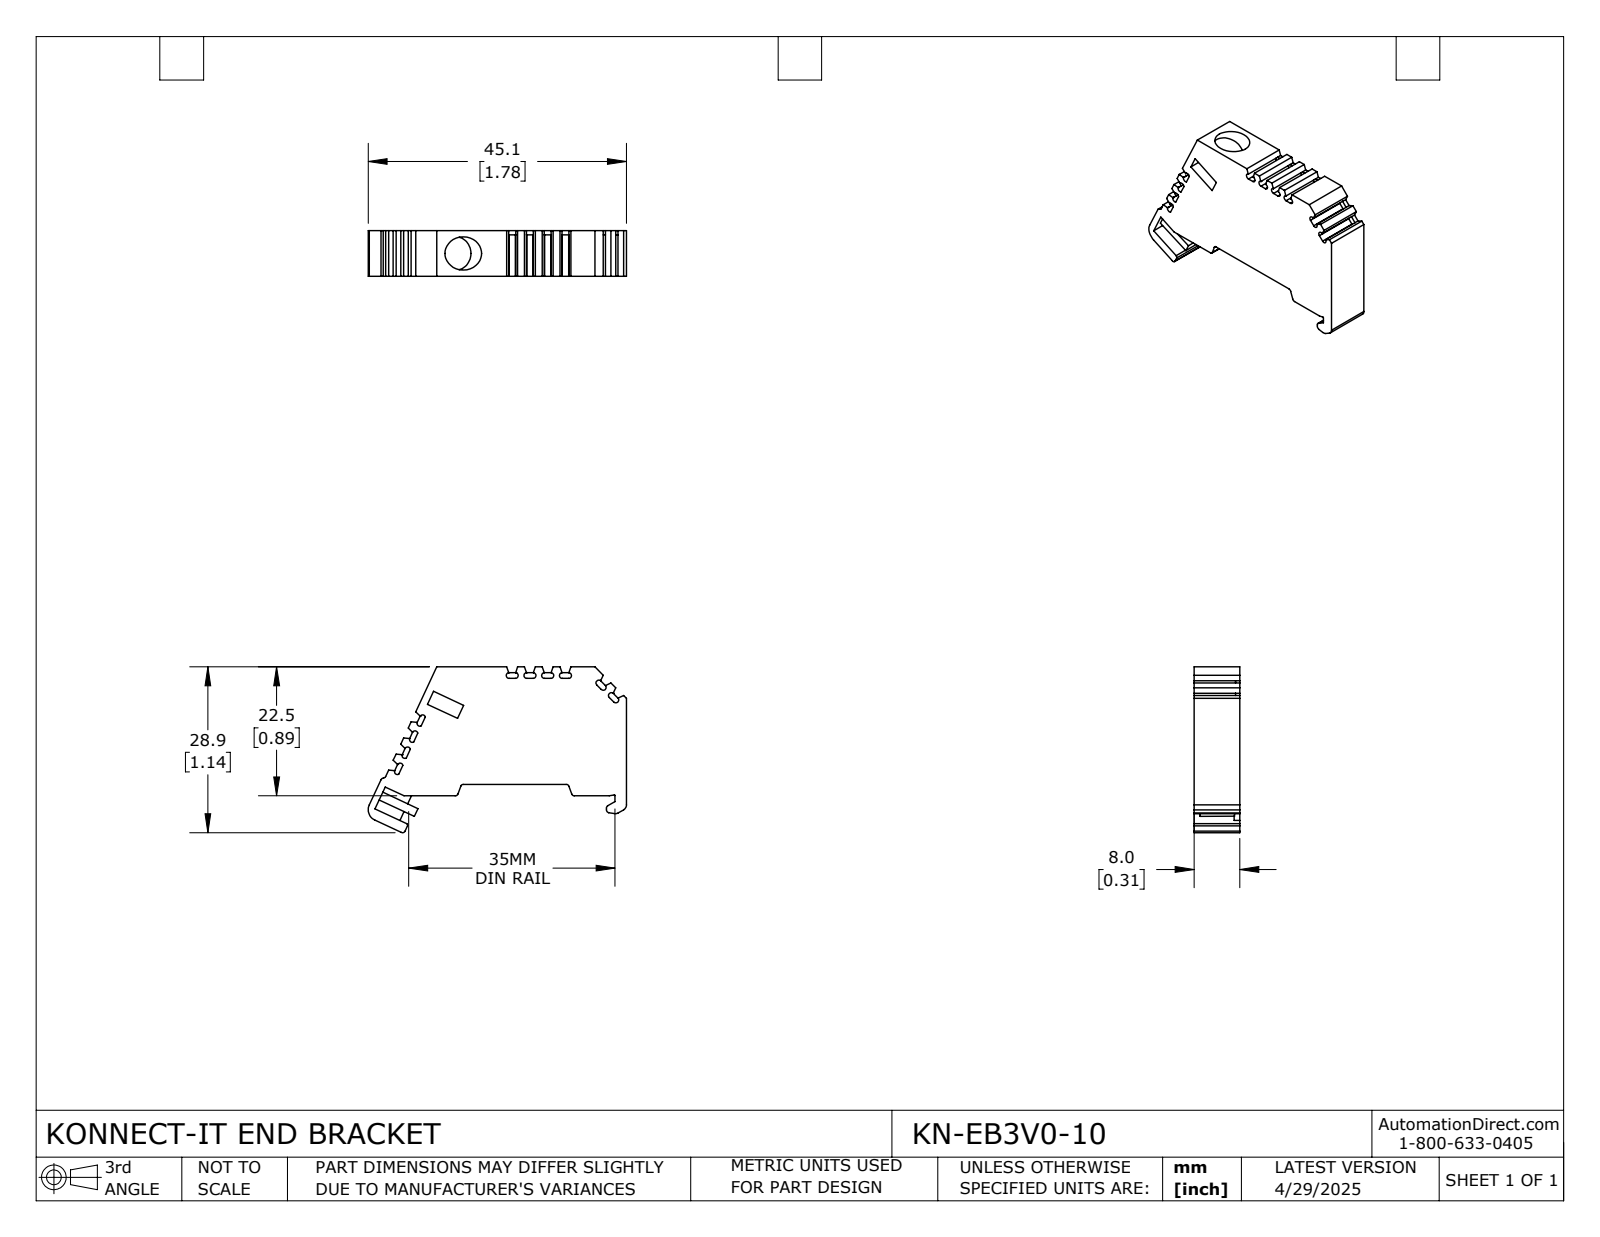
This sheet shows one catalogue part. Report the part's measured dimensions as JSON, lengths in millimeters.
{"part_name": "KN-EB3V0-10", "step_written_by": "SolidWorks 2024 (CONFIG_CONTROL_DESIGN)", "units": "millimeters", "bodies": {"solids": 1, "faces": 161, "planar": 116, "cylindrical": 45, "other": 0}, "overall_size": [45.09, 28.94, 8], "volume_mm3": 6266, "surface_area_mm2": 3463, "round_holes": [[3, 1], [5.8, 1]], "partial_cylinders_radius": [[0.5, 29], [1, 2], [0.1, 1], [0.3, 1], [2, 1]], "face_to_face_distances": [8, 2, 20.5, 22.5, 2.93, 2.5, 18.7, 1, 1.9, 20.4]}
